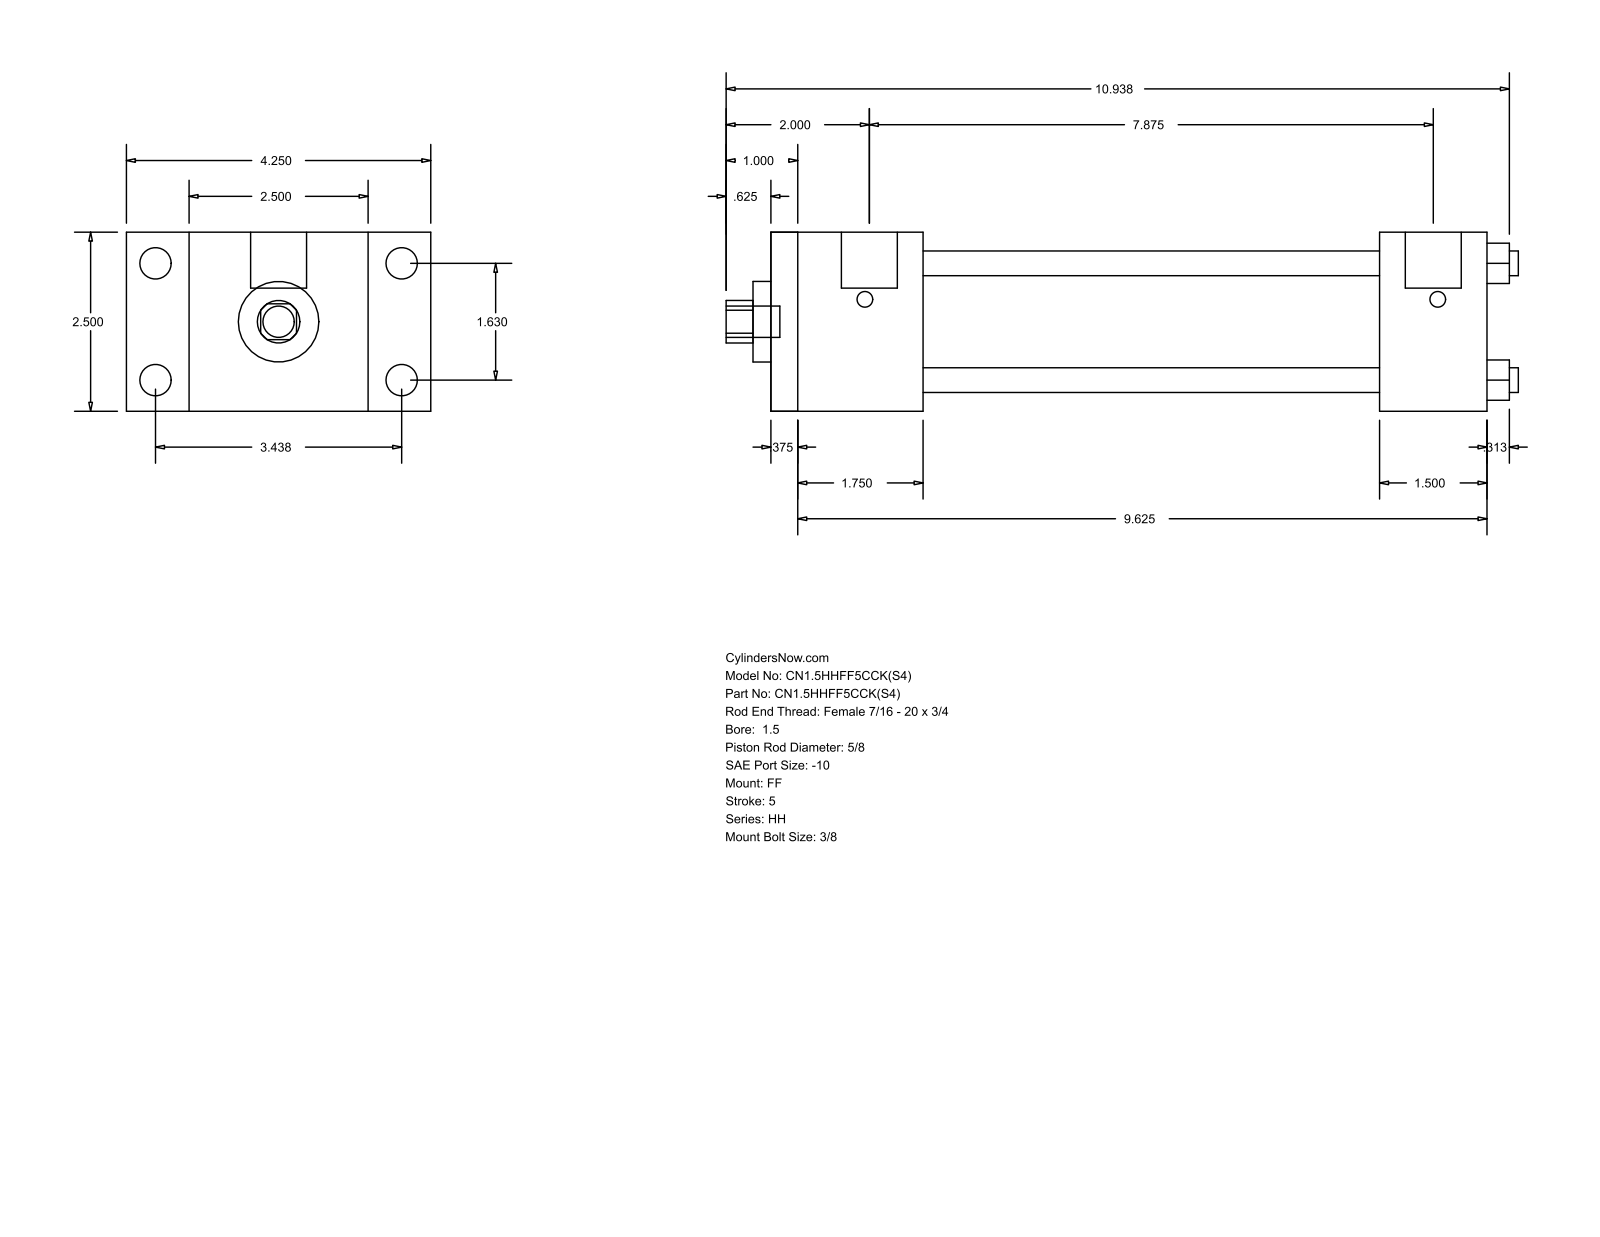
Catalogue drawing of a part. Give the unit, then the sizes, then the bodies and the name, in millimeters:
Units: millimetres
Overall size (bounding box): 280.99 × 107.95 × 63.5
Round holes (diameter × count): ⌀8.76 ×4, ⌀15.88 ×1, ⌀28.57 ×1, ⌀44.45 ×1
Round bosses / shafts (diameter × count): ⌀11.13 ×4, ⌀5.56 ×4, ⌀19.84 ×2, ⌀11.11 ×1
Partial cylindrical surfaces — rounded edges, fillets, slot ends (radius × count): R7.54 ×1
Main face-to-face distances: 63.5, 254, 9.52, 38.1, 244.48, 53.97, 44.45, 200.03, 215.9, 206.38
Hole centre spacings: 29.27, 41.4, 58.55
Bodies: 0 solids, 92 faces (64 planar, 28 cylindrical, 0 other)
Part name (STEP PRODUCT): HH_FF__0150_0.625
STEP written by: GSSL Pune (CONFIG_CONTROL_DESIGN)
